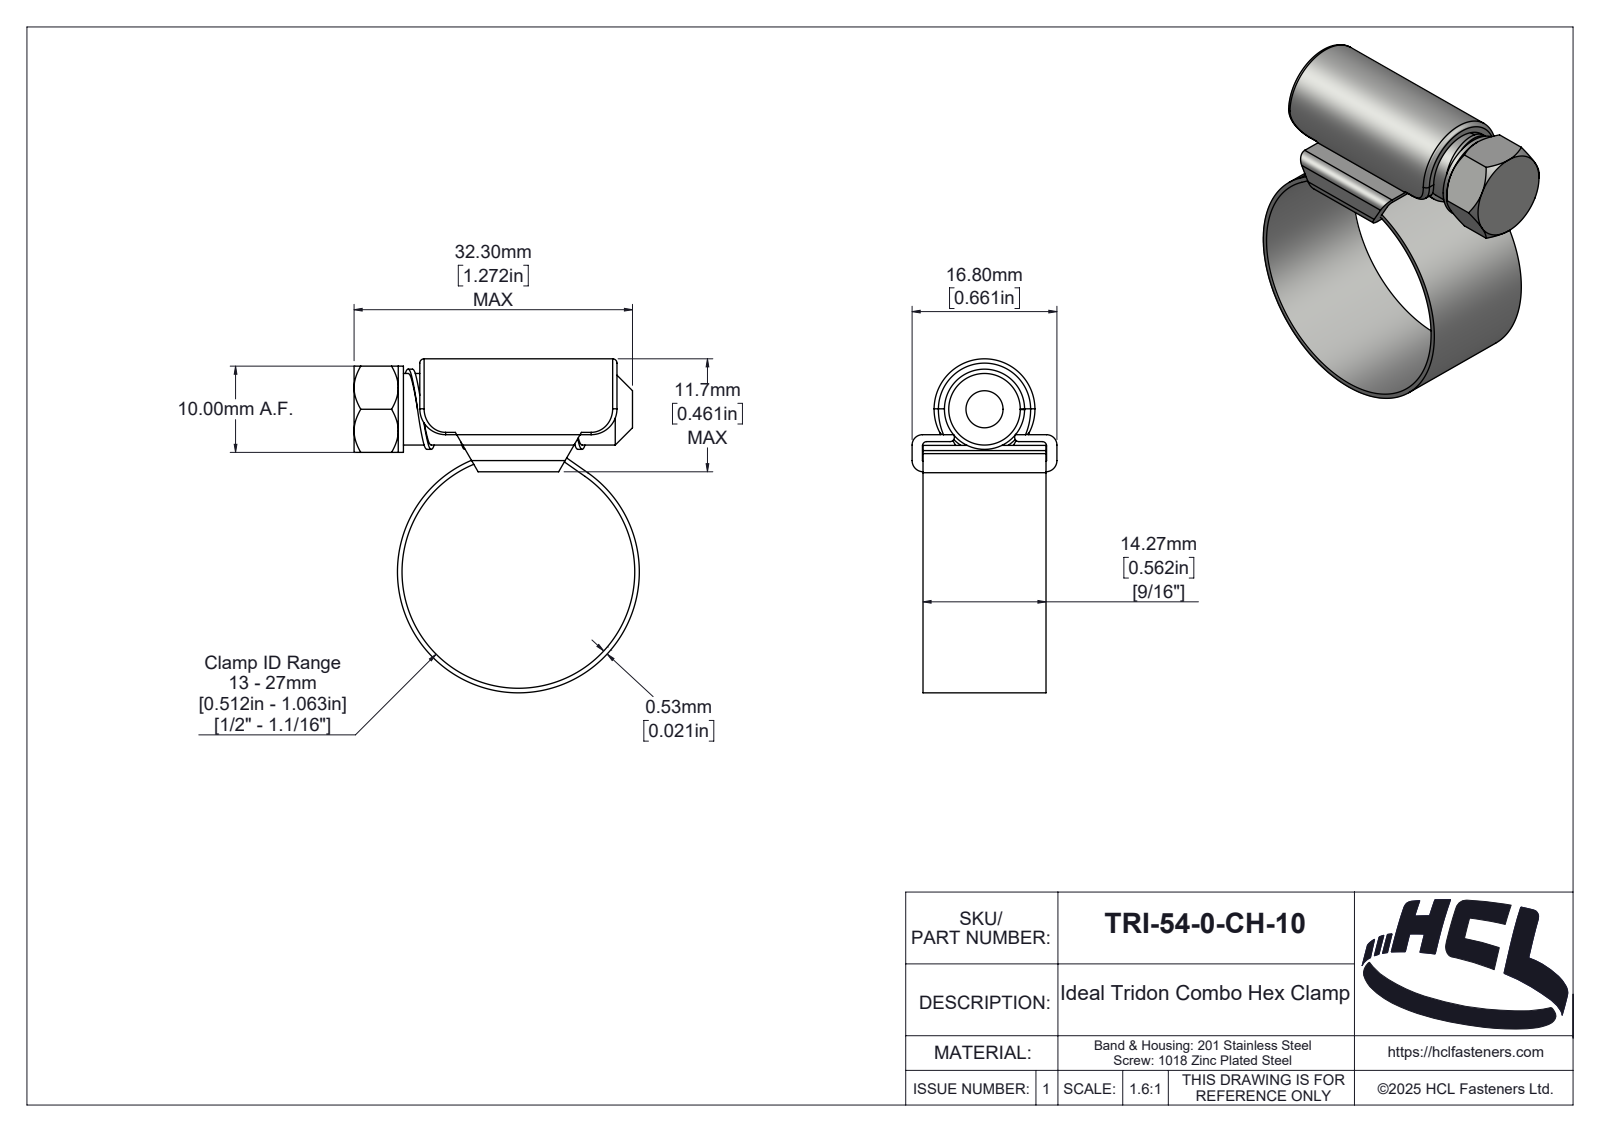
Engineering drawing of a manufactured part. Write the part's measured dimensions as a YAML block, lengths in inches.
part_name: "TRI-54-0-CH-10"
step_written_by: "SolidWorks 2025 (AUTOMOTIVE_DESIGN)"
units: inches
bodies: {solids: 3, faces: 212, planar: 35, cylindrical: 101, other: 76}
overall_size: [1.525, 1.303, 0.661]
volume: 0.218
surface_area: 8.837
round_holes:
  - {diameter: 1.063, count: 1}
round_bosses_or_shafts:
  - {diameter: 1.105, count: 1}
  - {diameter: 0.394, count: 1}
  - {diameter: 0.327, count: 1}
partial_cylinders:
  - {radius: 0.02, count: 6}
  - {radius: 0.118, count: 4}
  - {radius: 0.004, count: 2}
  - {radius: 0.047, count: 2}
  - {radius: 0.051, count: 2}
  - {radius: 0.018, count: 1}
  - {radius: 0.074, count: 1}
  - {radius: 0.079, count: 1}
face_to_face_distances: [0.047, 0.138, 0.091, 0.169, 0.122, 0.031, 0.021, 0.393, 0.561, 0.05]
